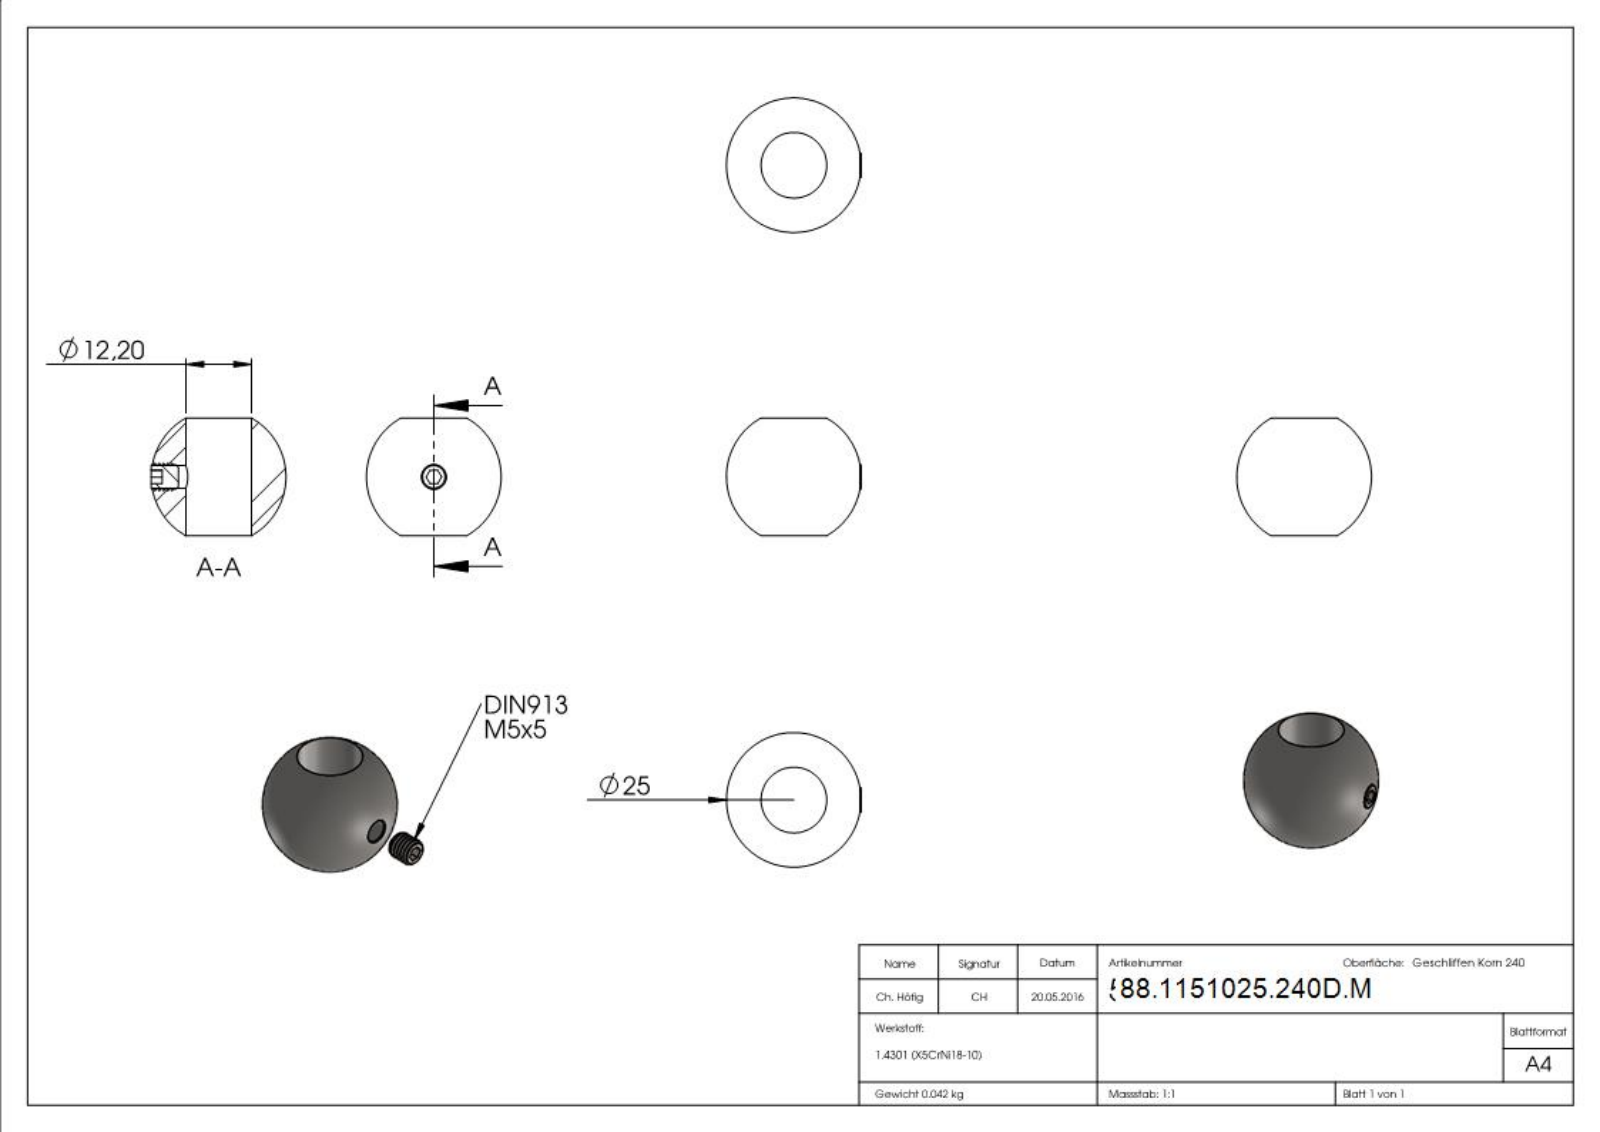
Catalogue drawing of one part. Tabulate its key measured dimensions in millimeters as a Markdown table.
| quantity | value |
| --- | --- |
| part name | socket set screw flat point_din_DIN 913 - M5 x 5-S; 51025-240D-M Teil1; socket set screw flat point_din; 51025-240D-M |
| STEP written by | SolidWorks 2018 (CONFIG_CONTROL_DESIGN) |
| units | millimeters |
| bodies | 2 solids, 34 faces (9 planar, 7 cylindrical, 18 other) |
| overall size | 25 × 25 × 21.39 |
| volume | 5 416 mm³ |
| surface area | 2 725 mm² |
| round holes (diameter × count) | 4.2 × 1, 12.2 × 1 |
| round bosses / shafts (diameter × count) | 5 × 1 |
| main face-to-face distances | 5, 2.5, 2, 3, 2.49 |
